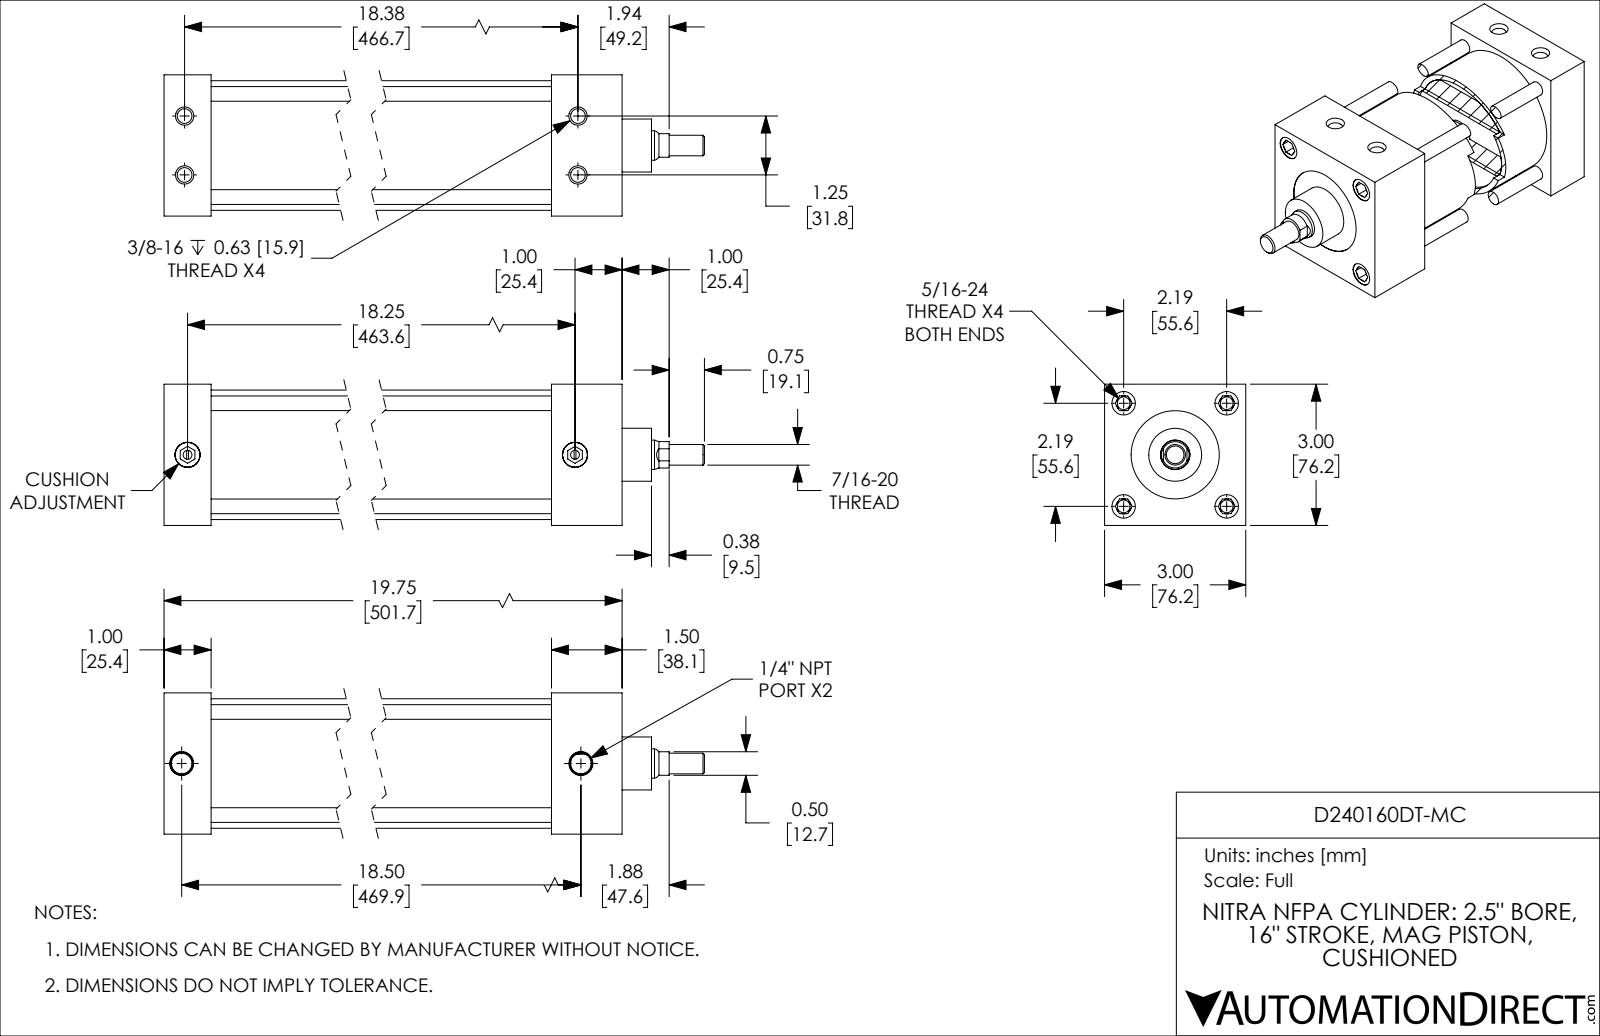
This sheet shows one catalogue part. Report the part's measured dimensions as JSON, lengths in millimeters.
{"part_name": "D240160DT-MC_CUSHION; D240160DT-MC; D240160DT-MC_BODY; D240160DT-MC_PISTON_KK1", "step_written_by": "SolidWorks 2019 (CONFIG_CONTROL_DESIGN)", "units": "millimeters", "bodies": {"solids": 4, "faces": 248, "planar": 90, "cylindrical": 78, "other": 80}, "overall_size": [546.1, 76.2, 76.2], "volume_mm3": 922400, "surface_area_mm2": 317600, "round_holes": [[6.9, 4], [8, 4], [12.7, 4], [4.8, 2], [11.1, 2], [13.5, 2], [15.9, 1], [47.6, 1], [63.5, 1]], "round_bosses_or_shafts": [[7.9, 4], [13.5, 2], [69.9, 1], [63.5, 1], [28.6, 1], [15.8, 1], [11.1, 1]], "partial_cylinders_radius": [[7.1, 1]], "face_to_face_distances": [76.2, 25.4, 463.6, 438.2, 501.7, 476.3, 38.1, 31.8, 57.2, 406.4], "hole_center_spacings": [39.3, 55.6, 468.6, 16, 16, 31.8, 78.7, 466.7]}
